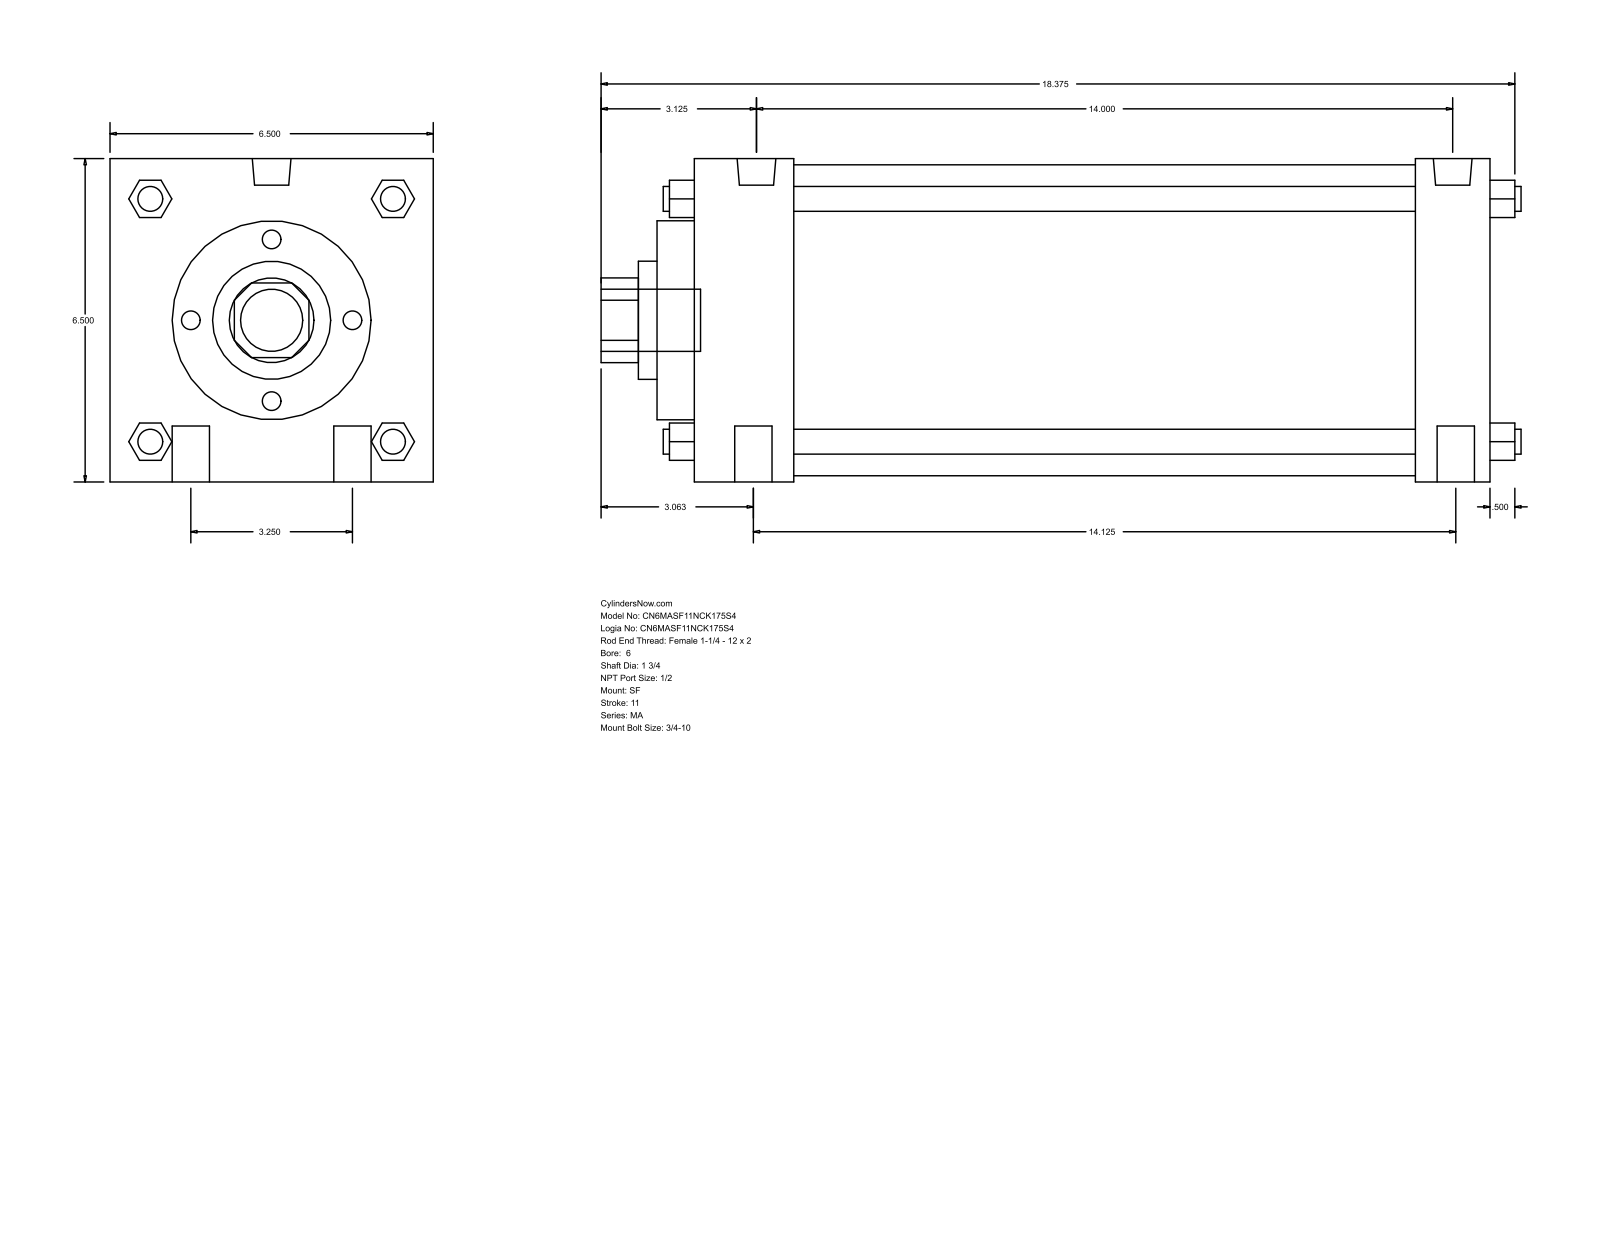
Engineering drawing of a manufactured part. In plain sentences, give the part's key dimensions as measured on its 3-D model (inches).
The part is named "MA_SF__0600_1.75". Its 3-D file was written by "GSSL Pune (CONFIG_CONTROL_DESIGN)". It is 0 solids with 126 faces: 95 planar, 31 cylindrical and 0 other. Overall it measures 18.5 by 6.5 by 6.5 inches. Round holes: 1 of diameter 1.75, 1 of diameter 2.375, 1 of diameter 4, 1 of diameter 6.25. Round bosses or shafts: 4 of diameter 0.75, 4 of diameter 0.5, 2 of diameter 0.778, 2 of diameter 0.687, 1 of diameter 1.25. Partial cylindrical surfaces (rounded edges, fillets, slot ends): 1 of radius 0.852. The main face-to-face distances are 6.5, 16, 0.75, 2, 14.5, 1.5, 12.5, 14, 2.75, 15.25.
